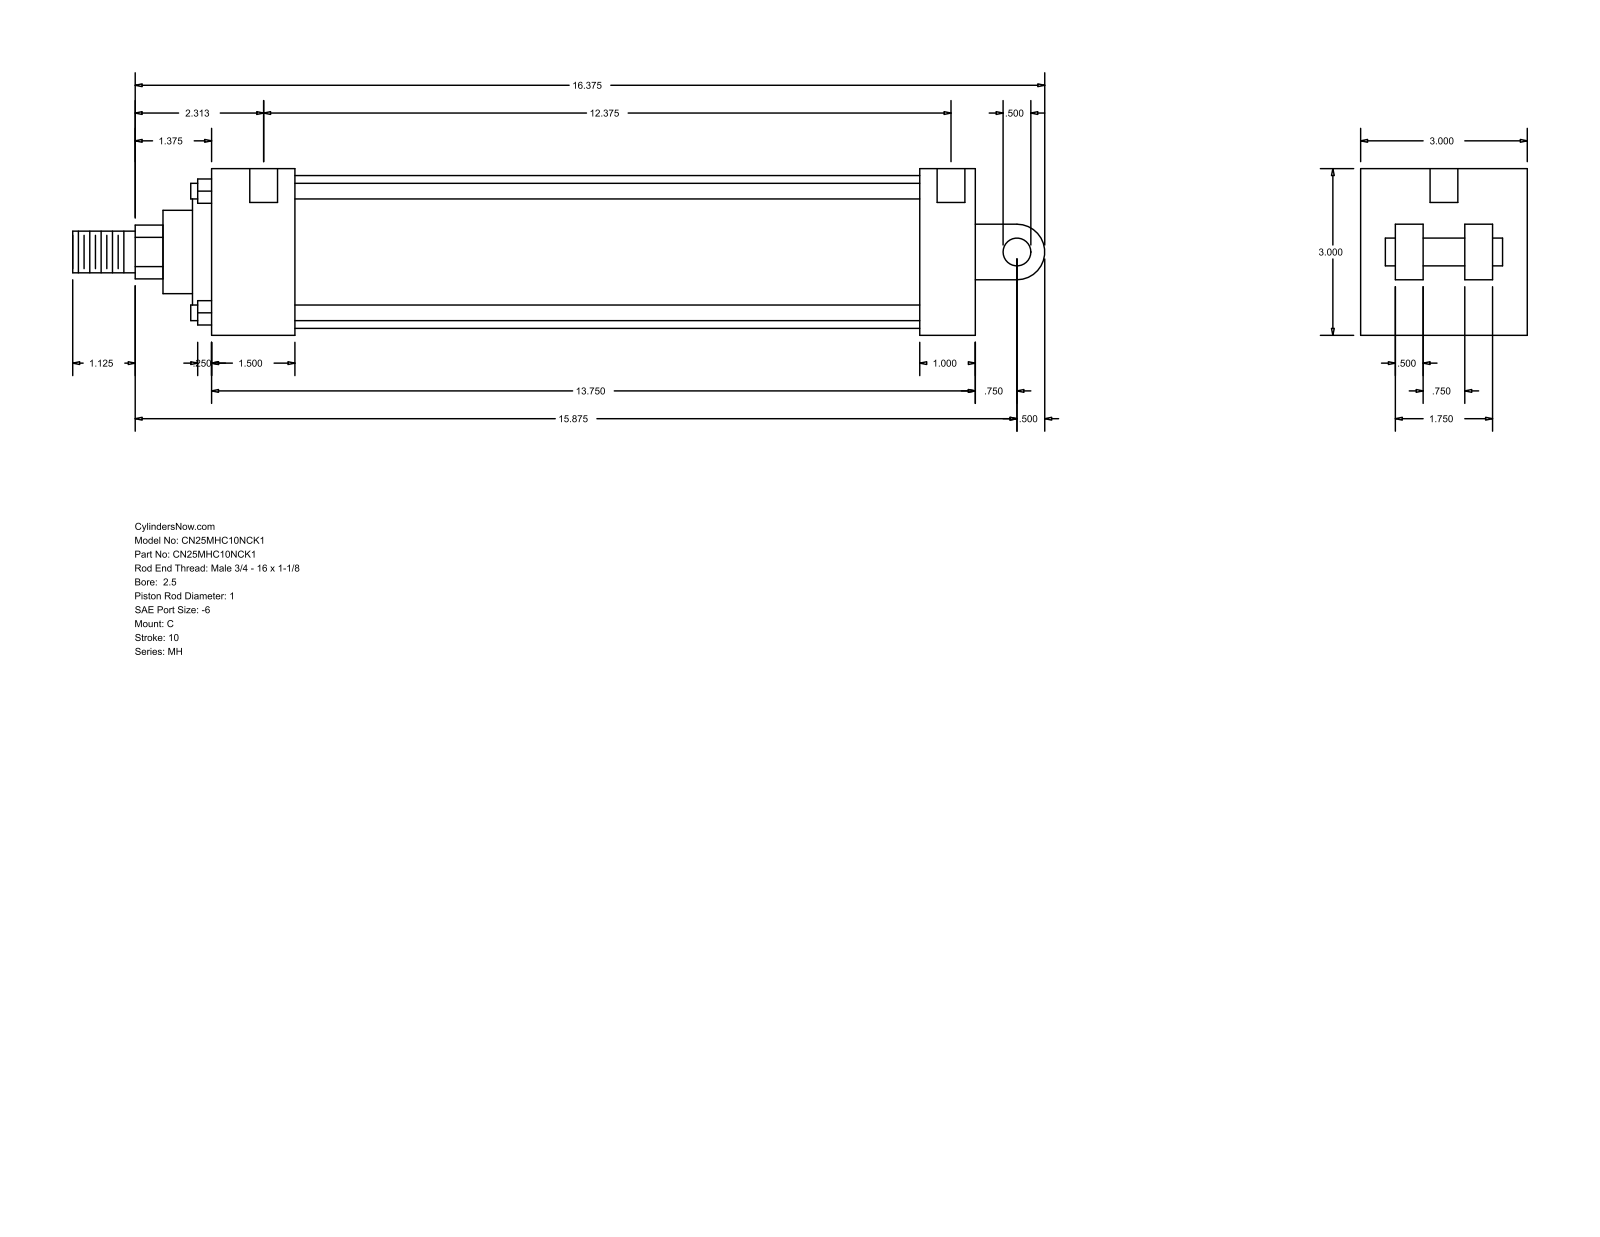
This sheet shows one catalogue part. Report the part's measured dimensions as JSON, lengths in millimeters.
{"part_name": "MH_C__0250_1", "step_written_by": "GSSL Pune (CONFIG_CONTROL_DESIGN)", "units": "millimeters", "bodies": {"solids": 0, "faces": 101, "planar": 71, "cylindrical": 30, "other": 0}, "overall_size": [444.5, 76.2, 76.2], "round_holes": [[5.56, 4], [12.7, 2]], "round_bosses_or_shafts": [[7.14, 4], [69.85, 1], [60.33, 1], [38.1, 1], [25.4, 1], [19.05, 1], [12.7, 1]], "partial_cylinders_radius": [[12.29, 1], [12.7, 1]], "face_to_face_distances": [76.2, 349.26, 60.33, 15.87, 323.85, 25.41, 38.11, 285.74, 311.15, 12.7], "hole_center_spacings": [322.26, 3.18, 4.76, 314.32, 317.5, 319.08]}
